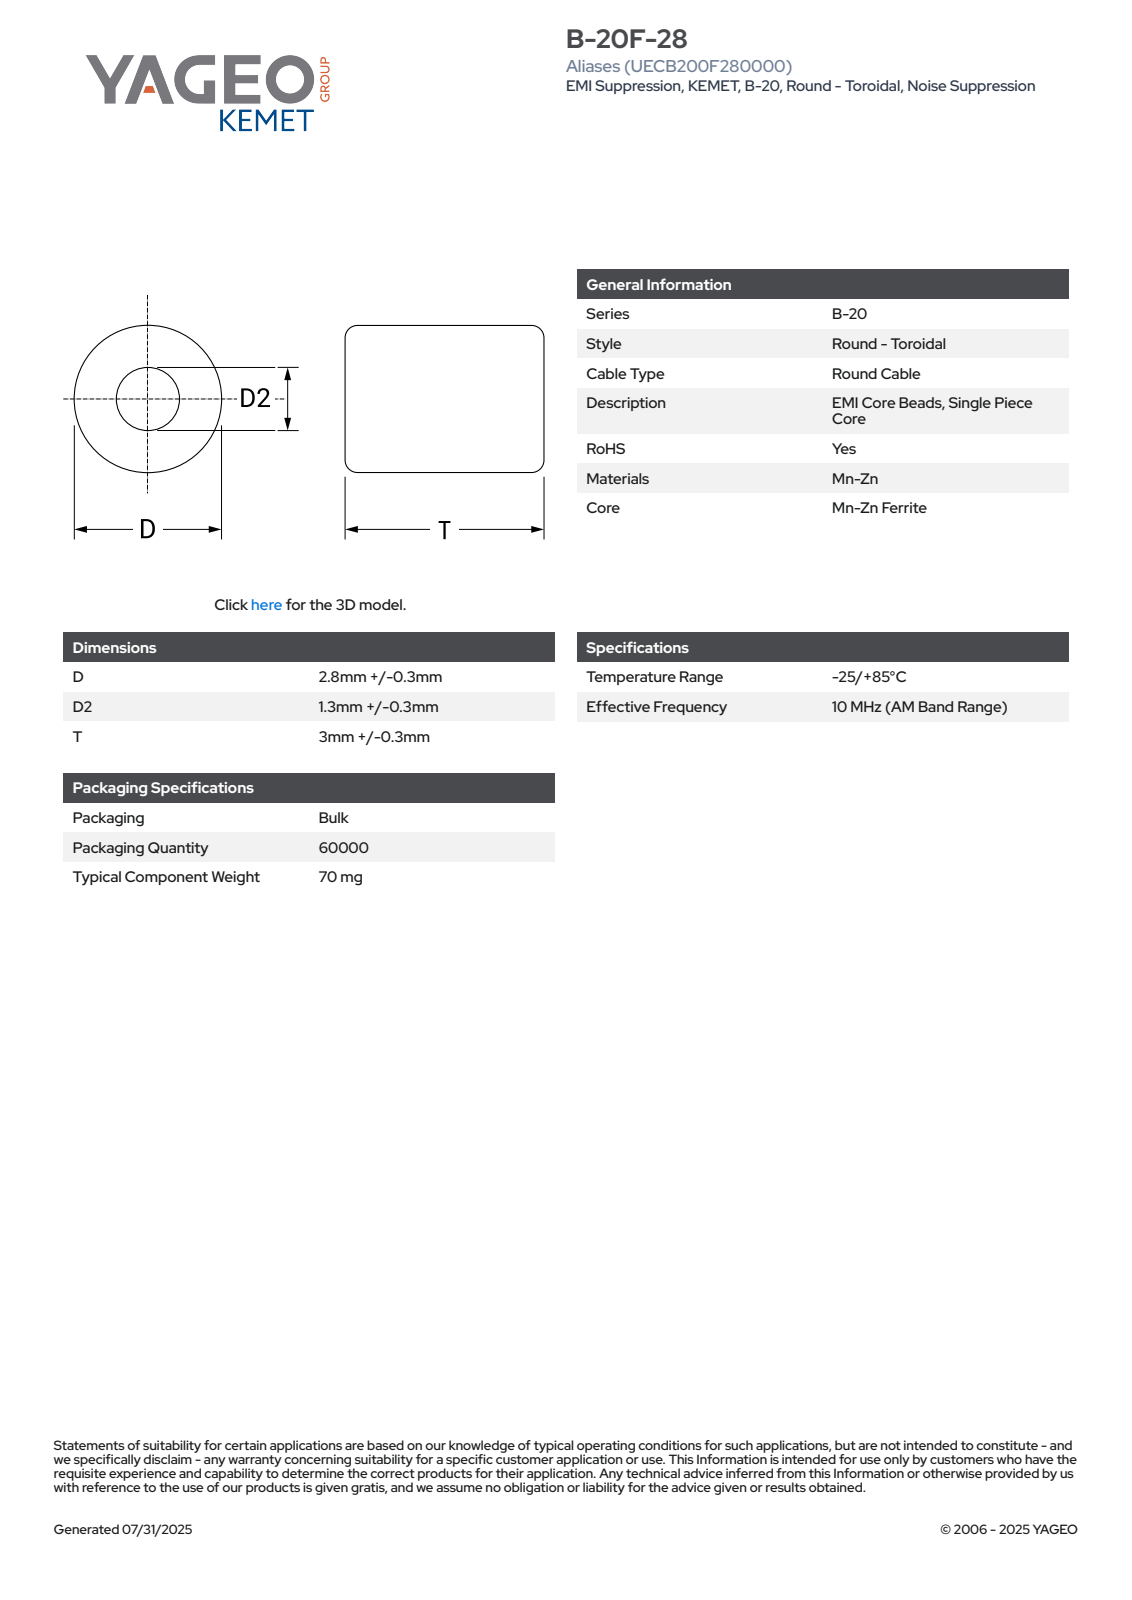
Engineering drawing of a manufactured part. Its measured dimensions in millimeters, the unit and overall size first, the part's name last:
Units: millimetres
Overall size (bounding box): 3.3 × 3.11 × 3.1
Round holes (diameter × count): ⌀1.3 ×1
Round bosses / shafts (diameter × count): ⌀3.1 ×1
Partial cylindrical surfaces — rounded edges, fillets, slot ends (radius × count): R1.56 ×1
Main face-to-face distances: 3.3, 1.46, 1.84, 0.38, 1.53, 1.77, 0.31, 1.7, 1.6, 1.63
Volume: 20 mm³ · Surface area: 57 mm²
Bodies: 1 solid, 66 faces (25 planar, 7 cylindrical, 34 other)
Part name (STEP PRODUCT): EC_KBCH_D3.1D21.3T3.3
STEP written by: SolidWorks 2021 (AUTOMOTIVE_DESIGN)
